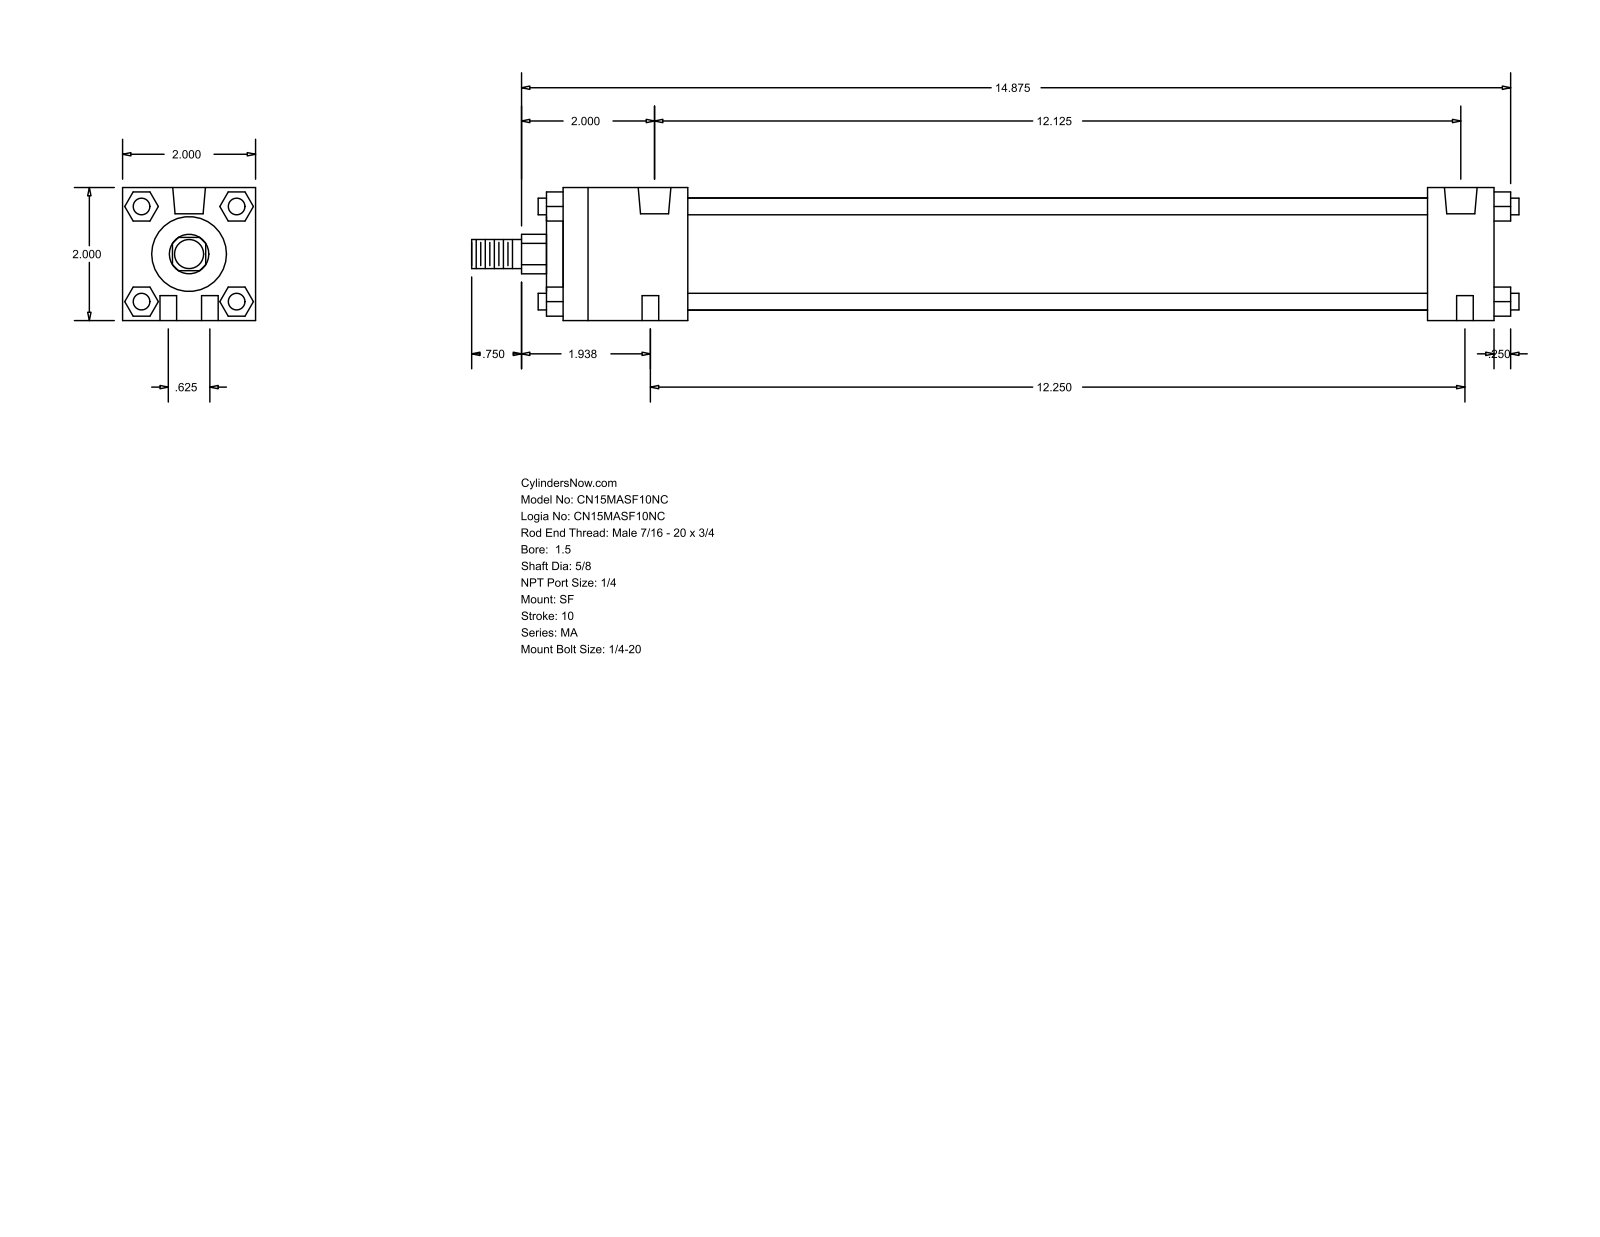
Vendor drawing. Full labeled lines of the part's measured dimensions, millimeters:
Part name (STEP PRODUCT): MA_SF__0150_0.625
STEP written by: GSSL Pune (CONFIG_CONTROL_DESIGN)
Units: millimetres
Bodies: 0 solids, 124 faces (94 planar, 30 cylindrical, 0 other)
Overall size (bounding box): 400.05 × 50.8 × 50.8
Round holes (diameter × count): ⌀6.35 ×4, ⌀7.94 ×2, ⌀12.49 ×2
Round bosses / shafts (diameter × count): ⌀6.35 ×4, ⌀42.93 ×1, ⌀28.57 ×1, ⌀15.88 ×1, ⌀11.11 ×1
Partial cylindrical surfaces — rounded edges, fillets, slot ends (radius × count): R7.54 ×1
Main face-to-face distances: 50.8, 355.6, 47.62, 330.19, 282.57, 307.98, 25.41, 6.35, 53.97, 336.54
Hole centre spacings: 8.1, 309.66, 15.88, 307.97, 311.15, 311.55
